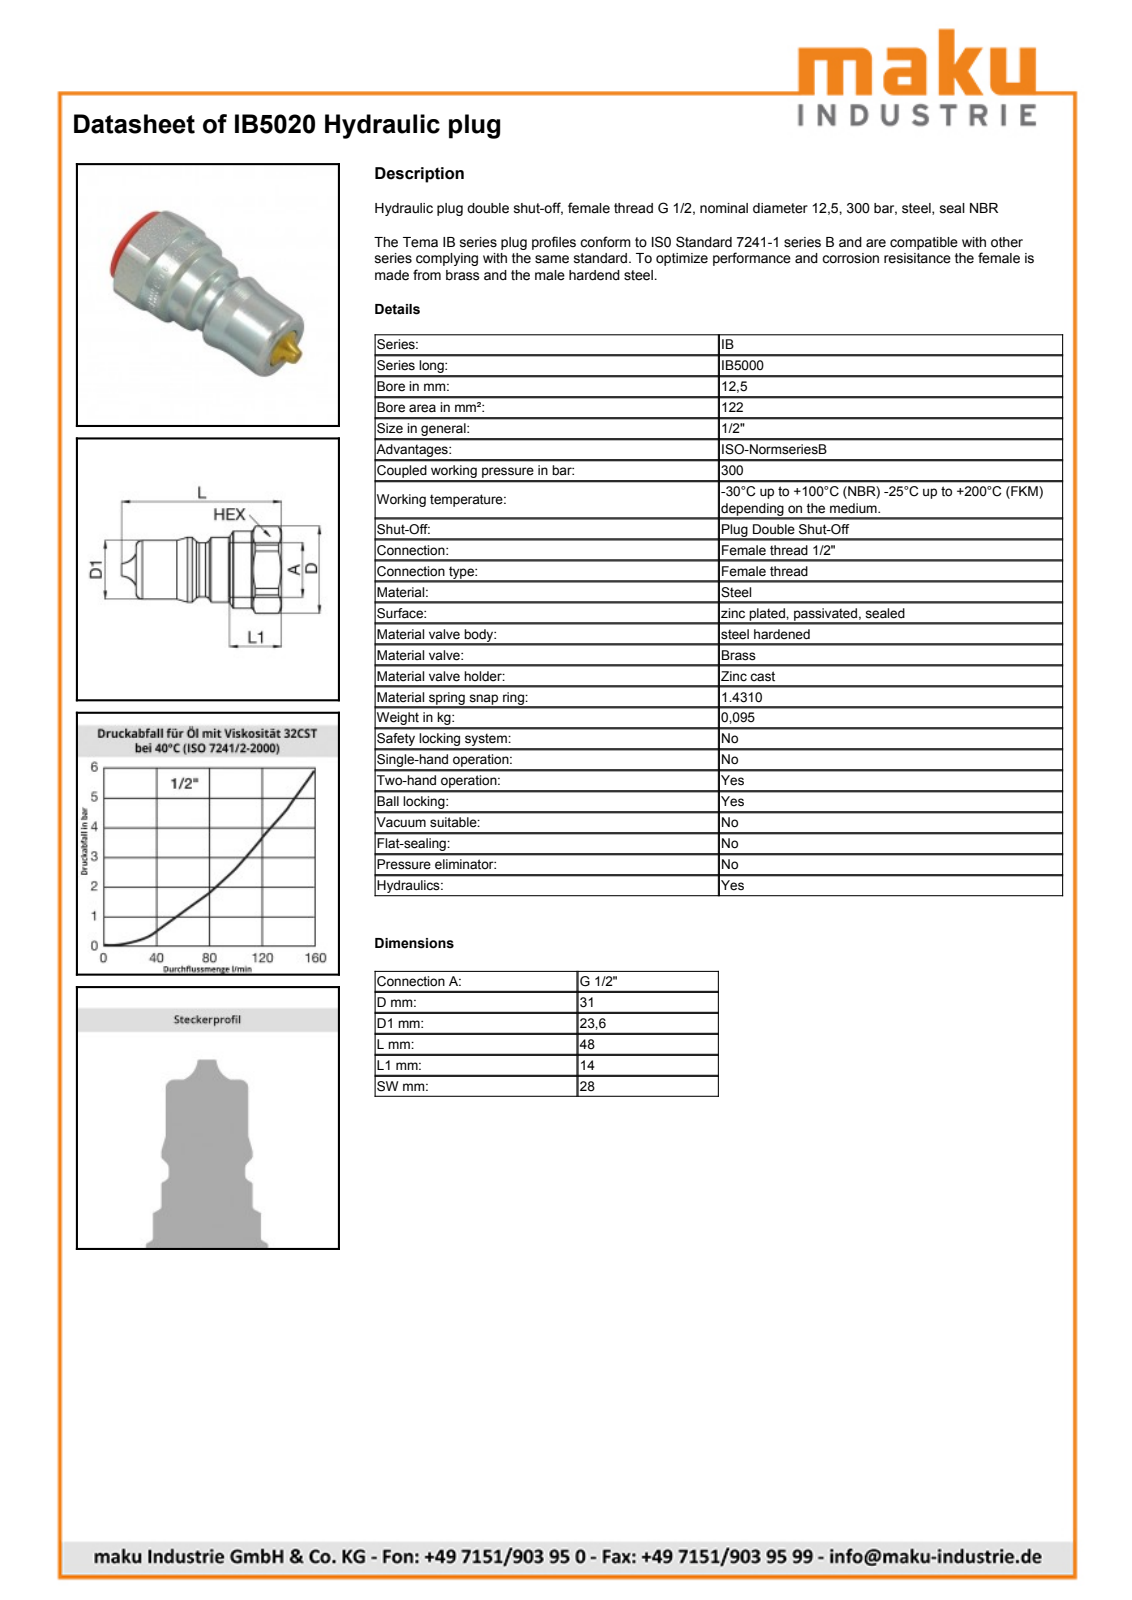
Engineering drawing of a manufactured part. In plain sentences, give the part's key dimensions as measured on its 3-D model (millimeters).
The part is named "IB5020". Its 3-D file was written by "SolidWorks 2009 (AUTOMOTIVE_DESIGN)". It is 1 solid with 55 faces: 10 planar, 19 cylindrical and 26 other. Overall it measures 46 by 30.7 by 28 millimeters. Its volume is 17 490 cubic millimeters and its surface area 5 572 square millimeters. Round holes: 1 of diameter 13.2, 1 of diameter 18.63. Round bosses or shafts: 1 of diameter 25.8, 1 of diameter 23.6, 1 of diameter 22.2. Partial cylindrical surfaces (rounded edges, fillets, slot ends): 1 of radius 15.35. The main face-to-face distances are 28, 15.65, 41.5, 25.85, 46, 30.35, 4.5.
